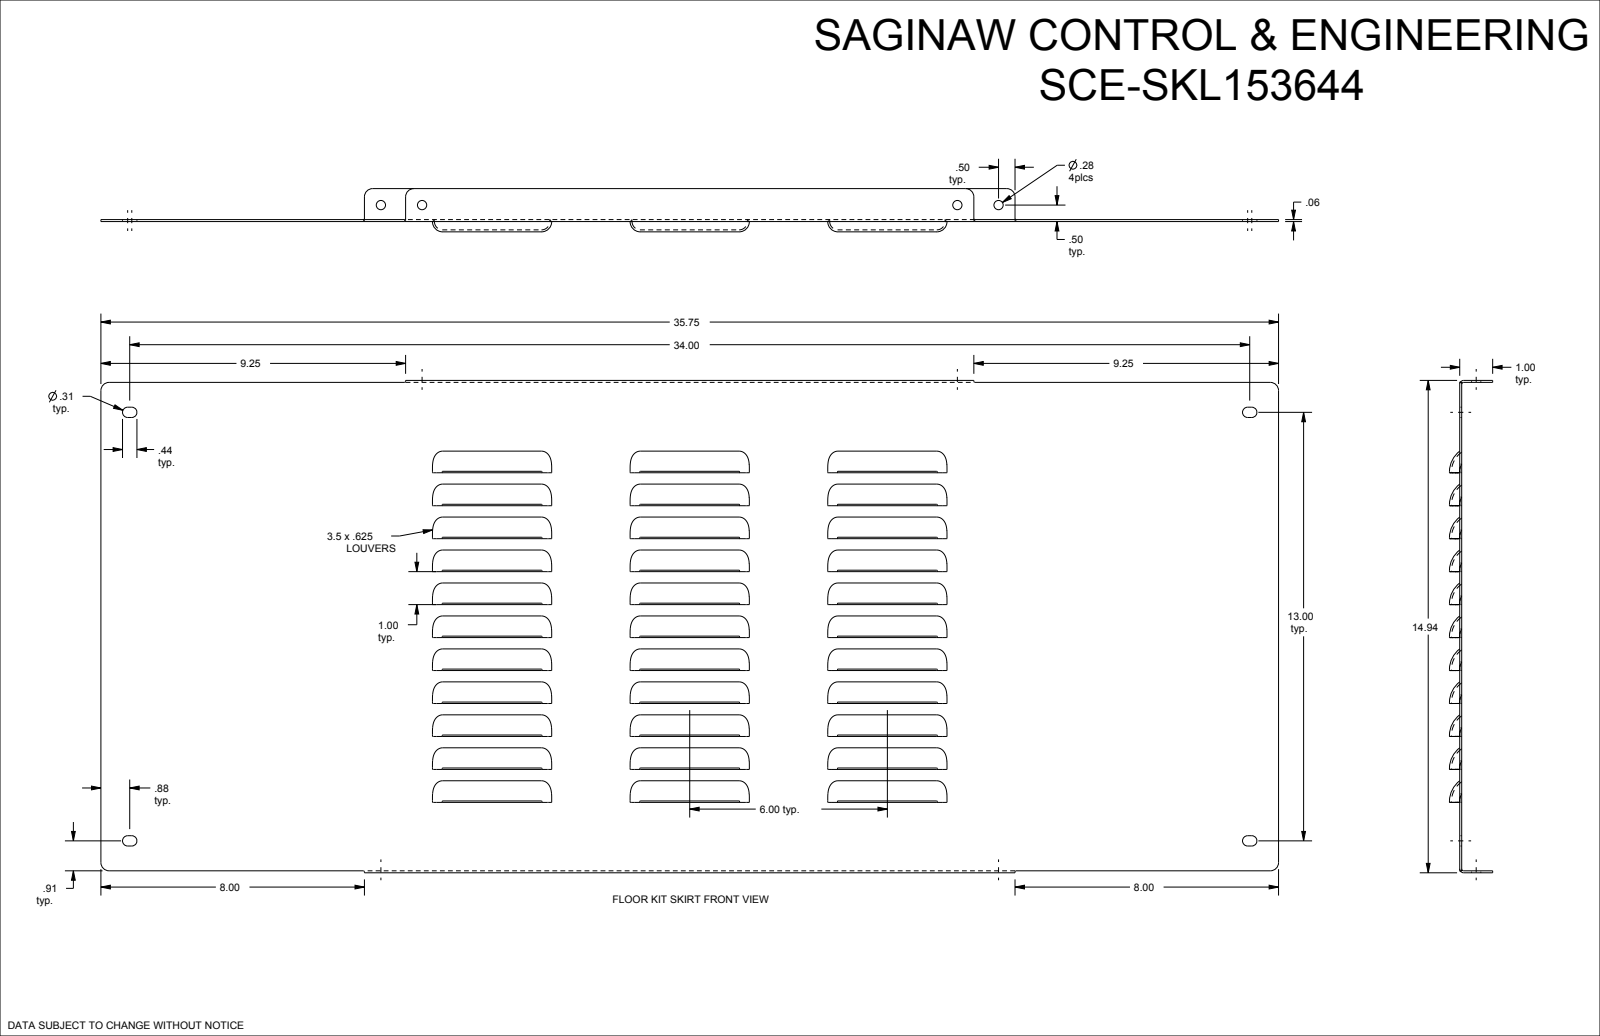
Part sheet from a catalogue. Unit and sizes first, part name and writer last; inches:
Units: inches
Overall size (bounding box): 35.75 × 14.938 × 1.31
Round holes (diameter × count): ⌀0.281 ×4
Partial cylindrical surfaces — rounded edges, fillets, slot ends (radius × count): R0.74 ×11, R0.8 ×11, R0.156 ×8, R0.25 ×8, R0.06 ×2, R0.12 ×2
Main face-to-face distances: 0.06, 0.06, 14.878, 14.817, 14.938, 1, 2, 3, 4, 5
Hole centre spacings: 1.25, 17.5, 16.25, 18.75
Volume: 35.34 in³ · Surface area: 1 197 in²
Bodies: 1 solid, 620 faces (254 planar, 90 cylindrical, 276 other)
Part name (STEP PRODUCT): SCE-SKL153644
STEP written by: SolidWorks 2021 (AUTOMOTIVE_DESIGN)
